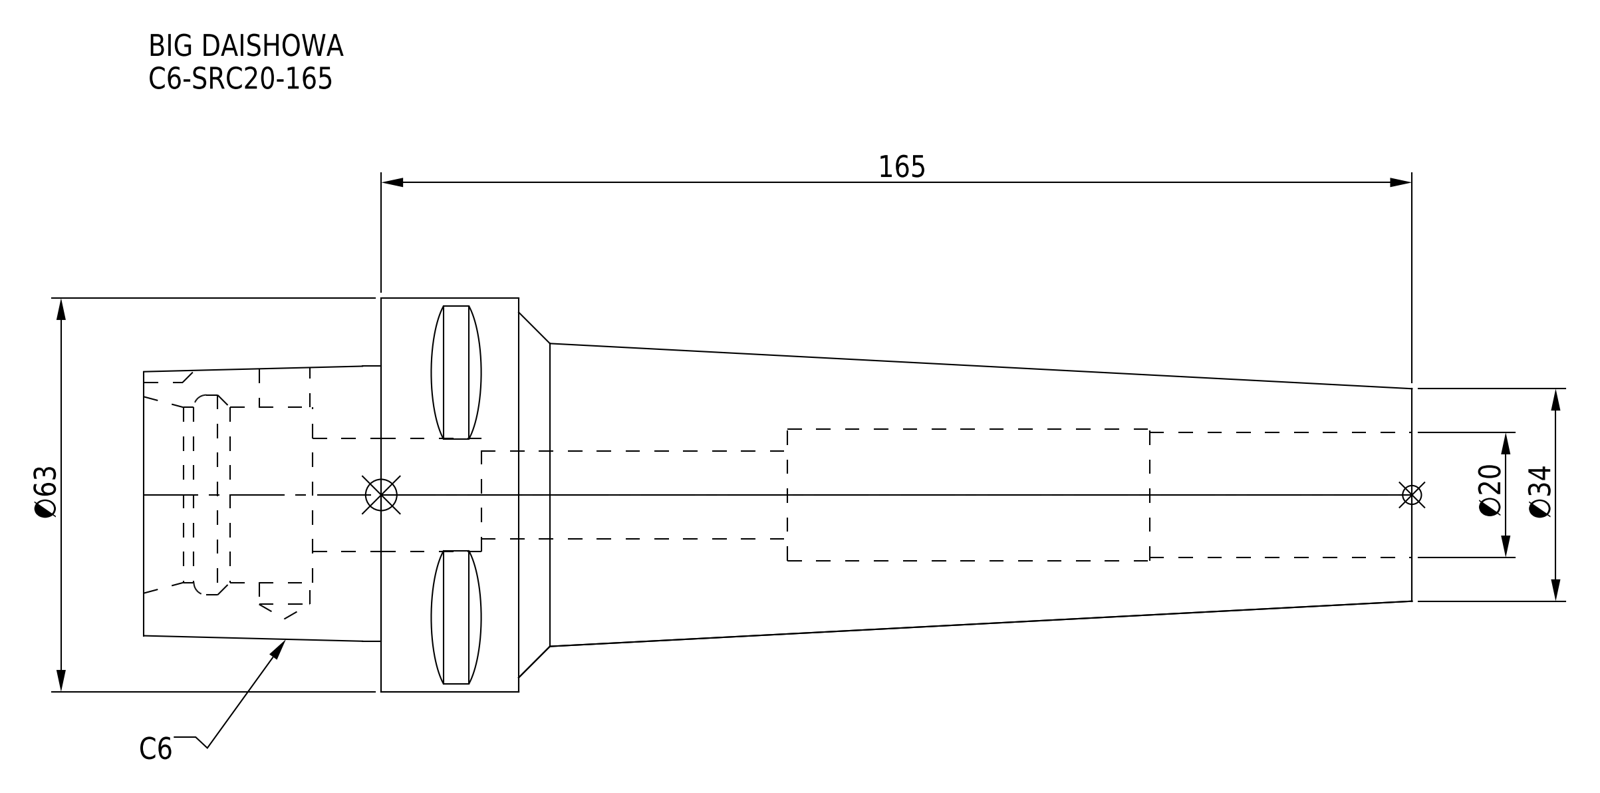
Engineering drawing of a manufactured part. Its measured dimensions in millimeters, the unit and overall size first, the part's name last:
Units: millimetres
Overall size (bounding box): 203 × 63 × 63
Round holes (diameter × count): ⌀8.1 ×1, ⌀14 ×1, ⌀18 ×1, ⌀20 ×1, ⌀21 ×1, ⌀28 ×1, ⌀32 ×1
Round bosses / shafts (diameter × count): ⌀63 ×1
Partial cylindrical surfaces — rounded edges, fillets, slot ends (radius × count): R5 ×1
Main face-to-face distances: 165, 203, 38, 27, 143, 22, 60, 176, 33, 11
Volume: 253 171 mm³ · Surface area: 45 838 mm²
Bodies: 1 solid, 65 faces (30 planar, 21 cylindrical, 14 other)
Part name (STEP PRODUCT): C6-SRC20-165
STEP written by: CREO PARAMETRIC BY PTC INC, 2016380 (AUTOMOTIVE_DESIGN)
